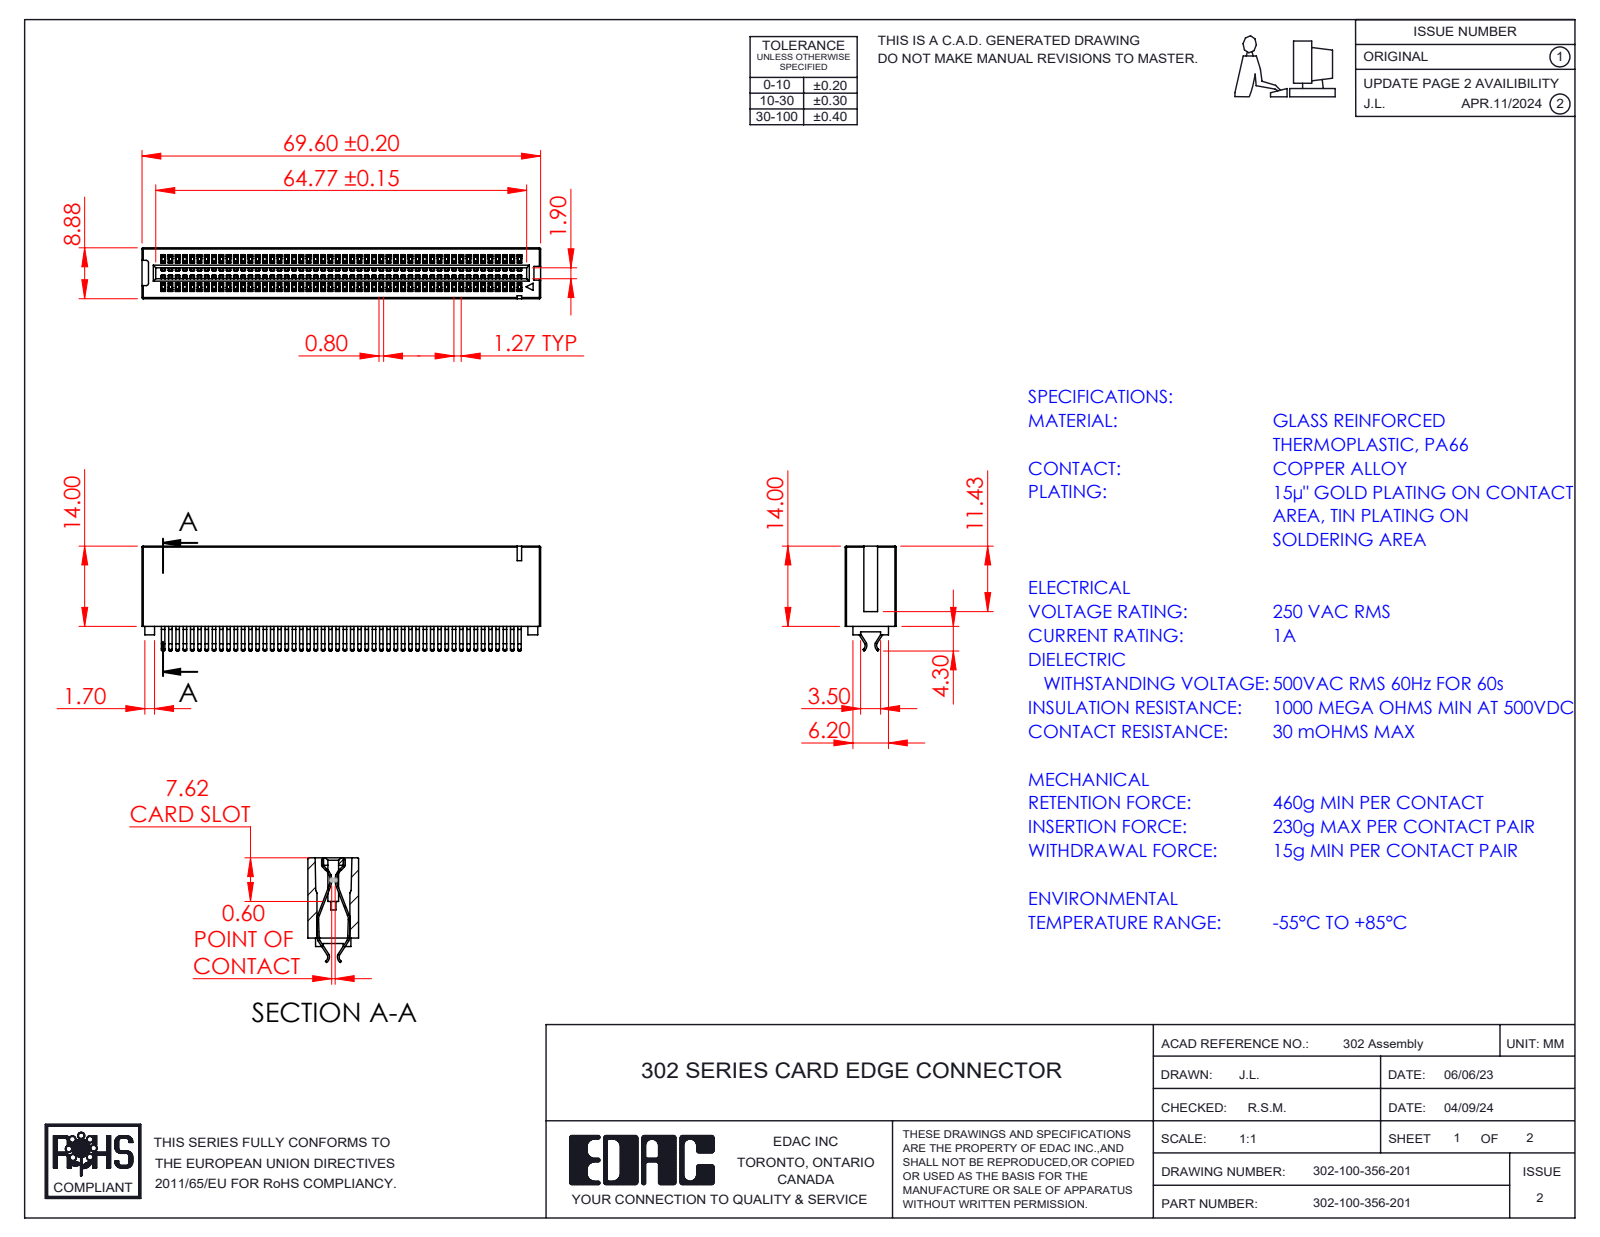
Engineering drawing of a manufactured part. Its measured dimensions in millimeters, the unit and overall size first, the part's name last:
Units: millimetres
Overall size (bounding box): 69.6 × 18.3 × 8.88
Partial cylindrical surfaces — rounded edges, fillets, slot ends (radius × count): R0.2 ×308, R0.11 ×2, R0.4 ×2, R0.41 ×2, R0.93 ×2, R1.05 ×2, R1.23 ×2, R1.25 ×2
Main face-to-face distances: 8.88, 1.27, 0.8, 2.54, 3.8, 0.47, 1.9, 3.49, 5.39, 3.81
Volume: 5 341 mm³ · Surface area: 15 223 mm²
Bodies: 101 solids, 4816 faces (3199 planar, 1613 cylindrical, 4 other)
Part name (STEP PRODUCT): 302-100-356-201; HSG_Vertical HSG; Contact_302-290-X56
STEP written by: SolidWorks 2023 (CONFIG_CONTROL_DESIGN)
